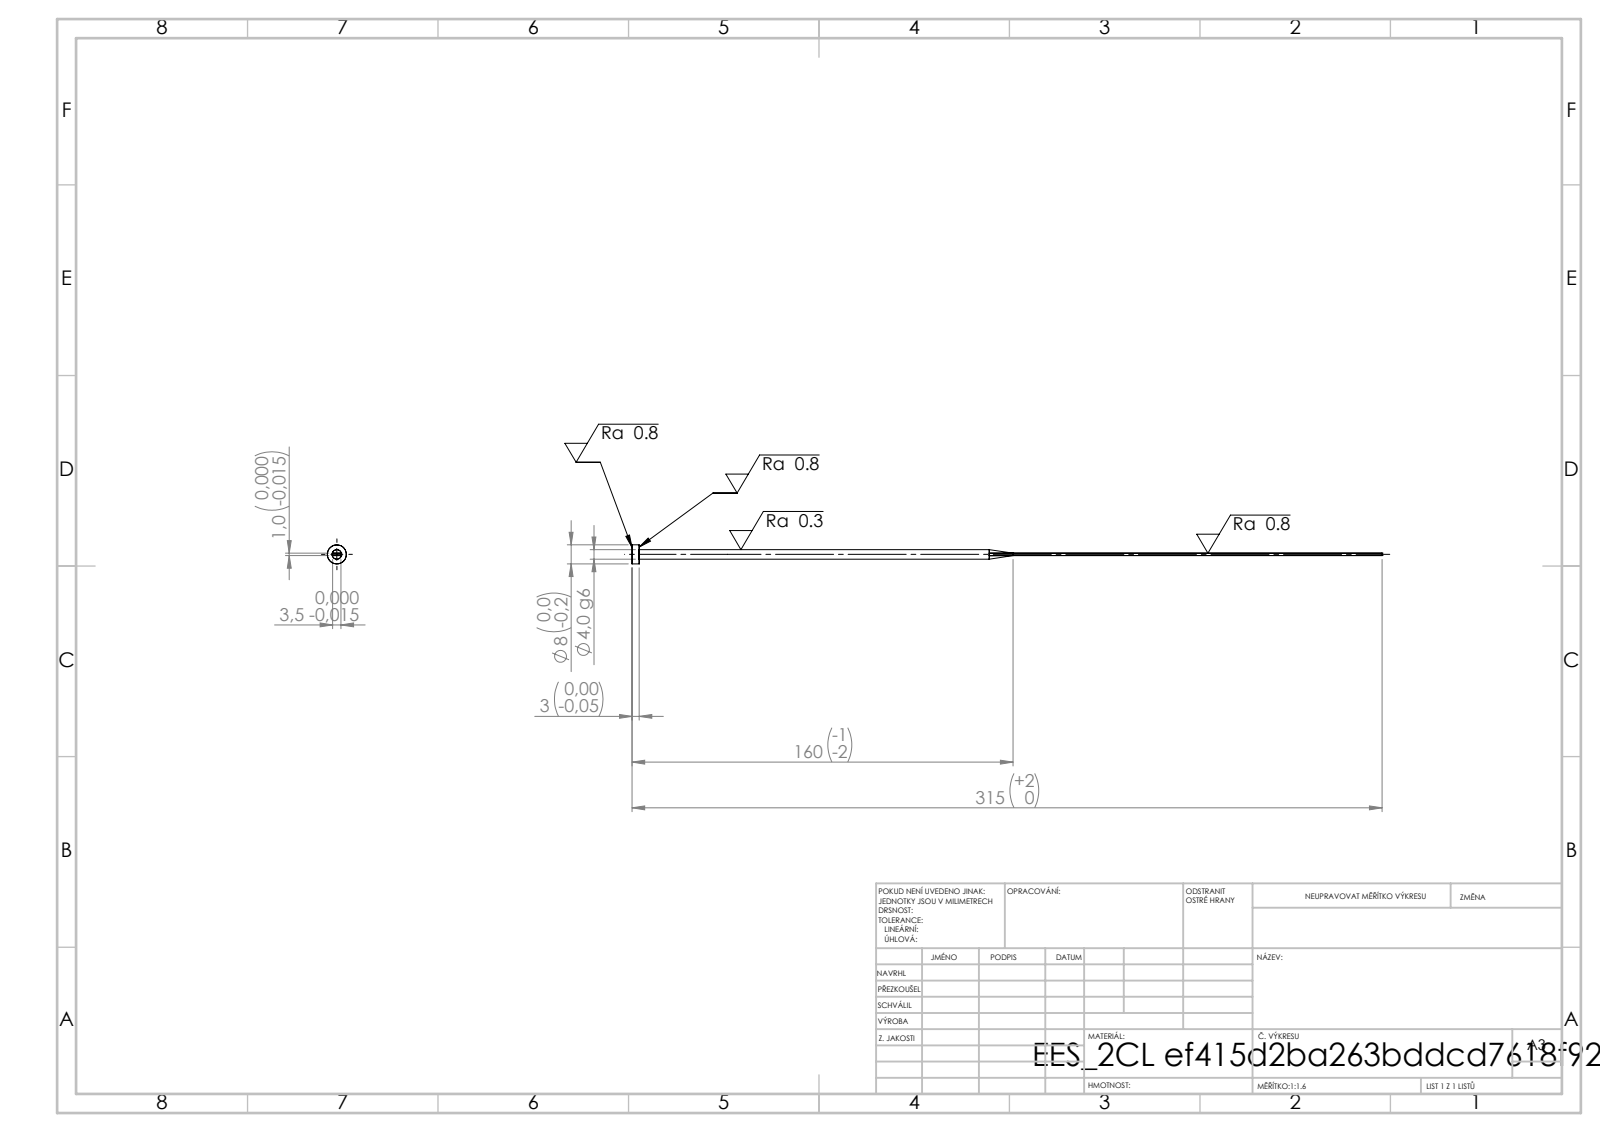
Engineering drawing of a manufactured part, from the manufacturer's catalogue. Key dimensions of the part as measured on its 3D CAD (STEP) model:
STEP written by: SolidWorks 2019 (CONFIG_CONTROL_DESIGN)
Units: millimetres
Bodies: 1 solid, 15 faces (7 planar, 4 cylindrical, 4 other)
Overall size (bounding box): 315 × 8 × 8
Volume: 2 617 mm³ · Surface area: 3 513 mm²
Round bosses / shafts (diameter × count): ⌀8 ×1, ⌀4 ×1
Main face-to-face distances: 1, 3.5, 3, 315, 312
